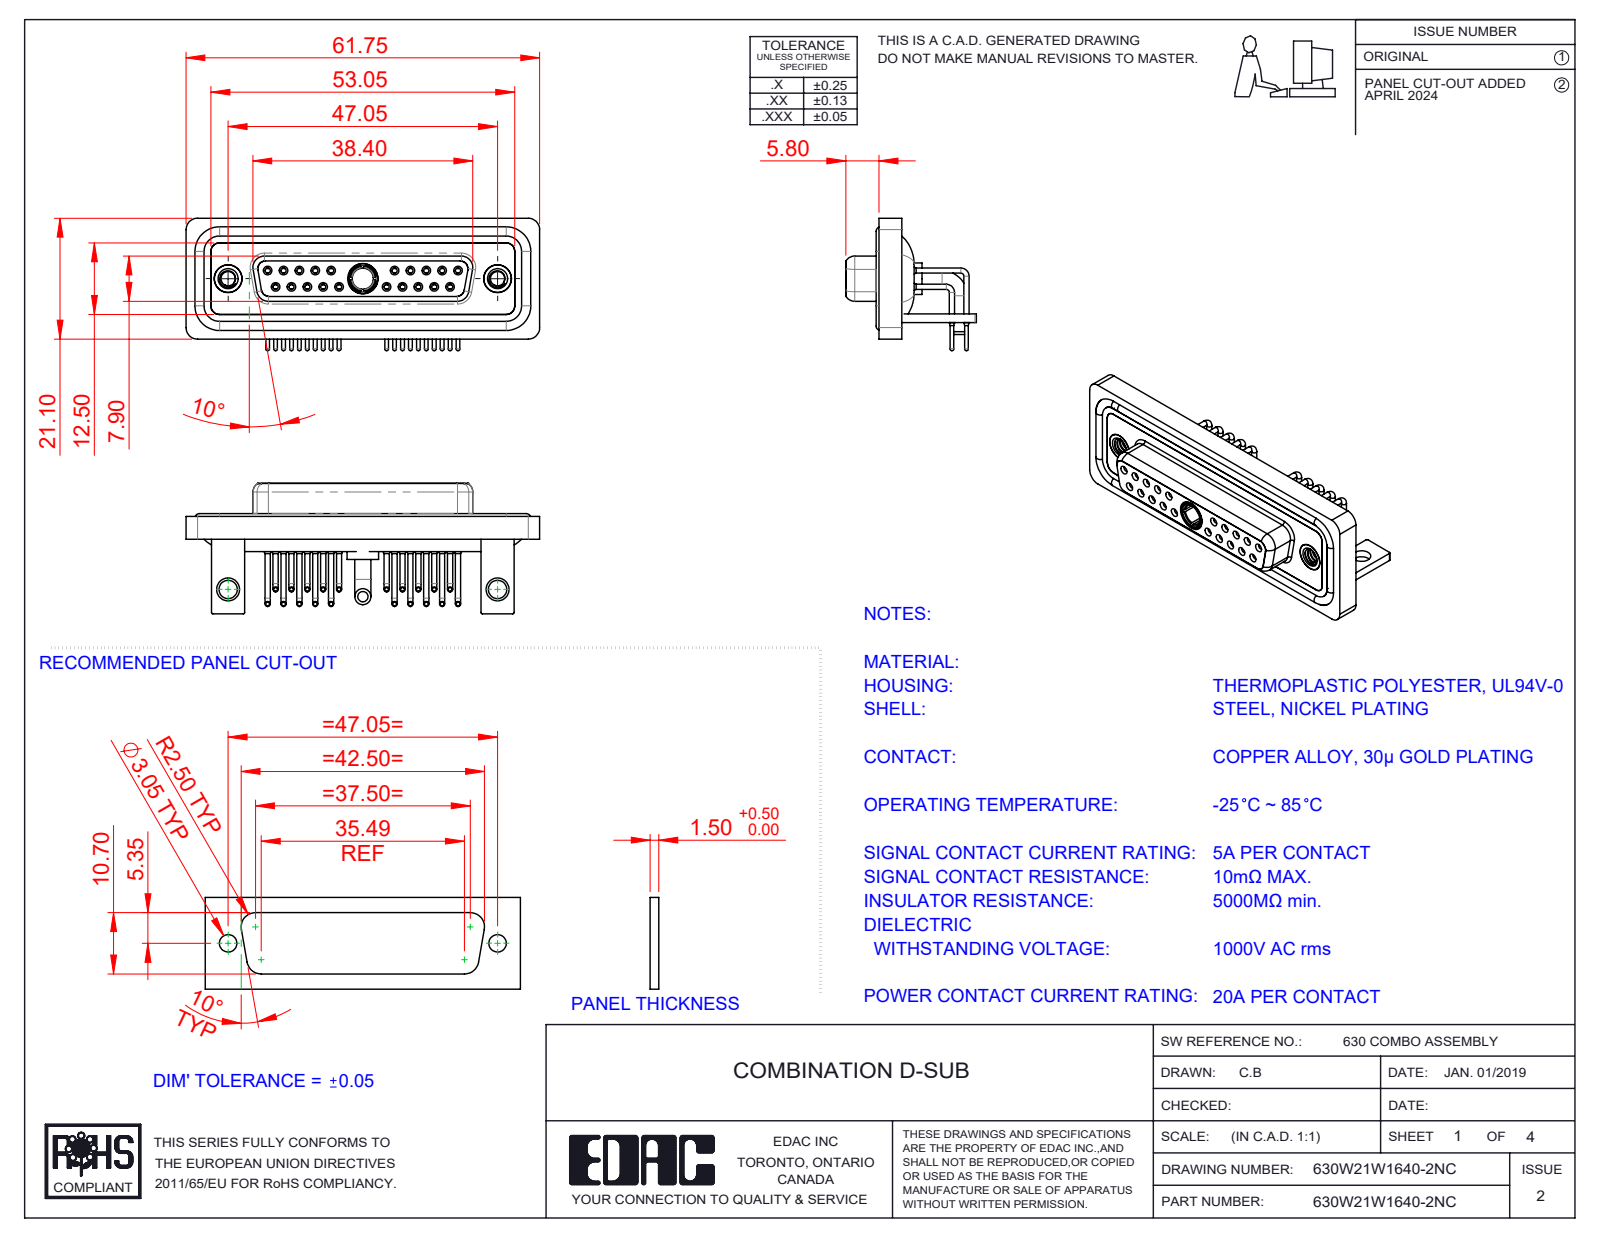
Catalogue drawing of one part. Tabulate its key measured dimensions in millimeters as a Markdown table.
| quantity | value |
| --- | --- |
| part name | 630Combo Threaded Rivet_A; 630Combo Housing_21W1; 630W21W1640-2NC; Power Socket_20A RA (+6 more) |
| STEP written by | SolidWorks 2023 (CONFIG_CONTROL_DESIGN) |
| units | millimeters |
| bodies | 31 solids, 1566 faces (454 planar, 695 cylindrical, 417 other) |
| overall size | 61.75 × 23.12 × 22.8 |
| volume | 8 865 mm³ |
| surface area | 15 518 mm² |
| round holes (diameter × count) | 0.9 × 20, 1.1 × 20, 1.5 × 20, 2 × 20, 1.6 × 10, 1.7 × 10, 4.85 × 3, 2.5 × 2, 3.2 × 2, 4 × 2, 4.05 × 2, 5 × 2 |
| round bosses / shafts (diameter × count) | 0.9 × 20, 0.65 × 20, 1.6 × 14, 4.95 × 2, 4.8 × 2, 2.8 × 2, 5.5 × 1, 5.2 × 1 |
| partial cylindrical surfaces (radius × count) | 2 × 19, 1.5 × 18, 0.25 × 16, 1.35 × 8, 1.6 × 8, 0.5 × 5, 0.6 × 4, 0.65 × 4 |
| main face-to-face distances | 0.4, 1.8, 2.9, 3.7, 1.5, 4.1, 1.1, 1.4, 1.6, 2.5 |
| hole center spacings | 3.16, 2.77, 5.54, 8.31, 5.04, 19.39, 20.97, 22.16 |
